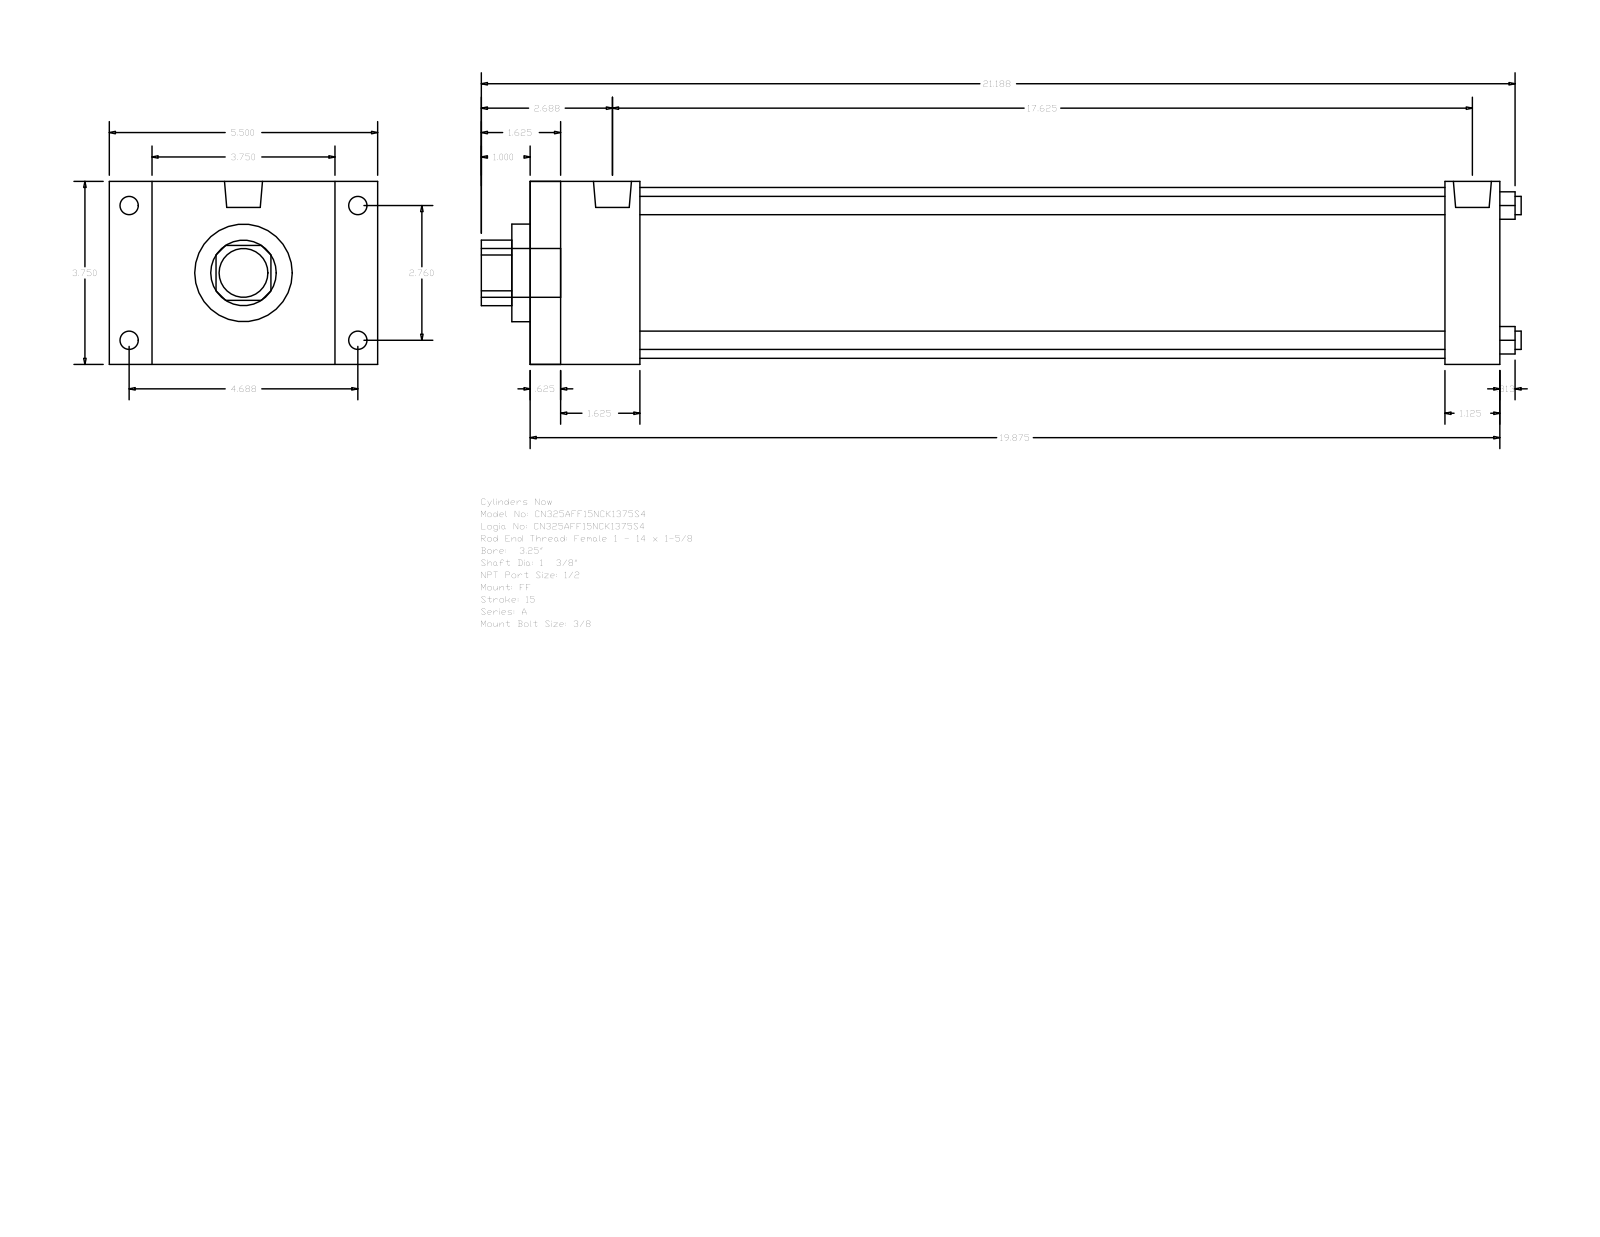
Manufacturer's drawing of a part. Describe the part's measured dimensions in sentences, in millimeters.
The part is named "A_FF__0325_1.375". Its 3-D file was written by "GSSL Pune (CONFIG_CONTROL_DESIGN)". It is 0 solids with 92 faces: 64 planar, 28 cylindrical and 0 other. Overall it measures 541.34 by 139.7 by 95.25 millimeters. Round holes: 4 of diameter 9.53, 1 of diameter 34.92, 1 of diameter 50.8, 1 of diameter 88.9. Round bosses or shafts: 4 of diameter 9.53, 4 of diameter 8.73, 2 of diameter 19.77, 1 of diameter 25.4. Partial cylindrical surfaces (rounded edges, fillets, slot ends): 1 of radius 17.06. The main face-to-face distances are 95.24, 504.83, 15.87, 488.96, 28.58, 22.23, 117.47, 57.15, 476.25, 41.28. The hole center spacings are 49.57, 70.1, 99.14.
